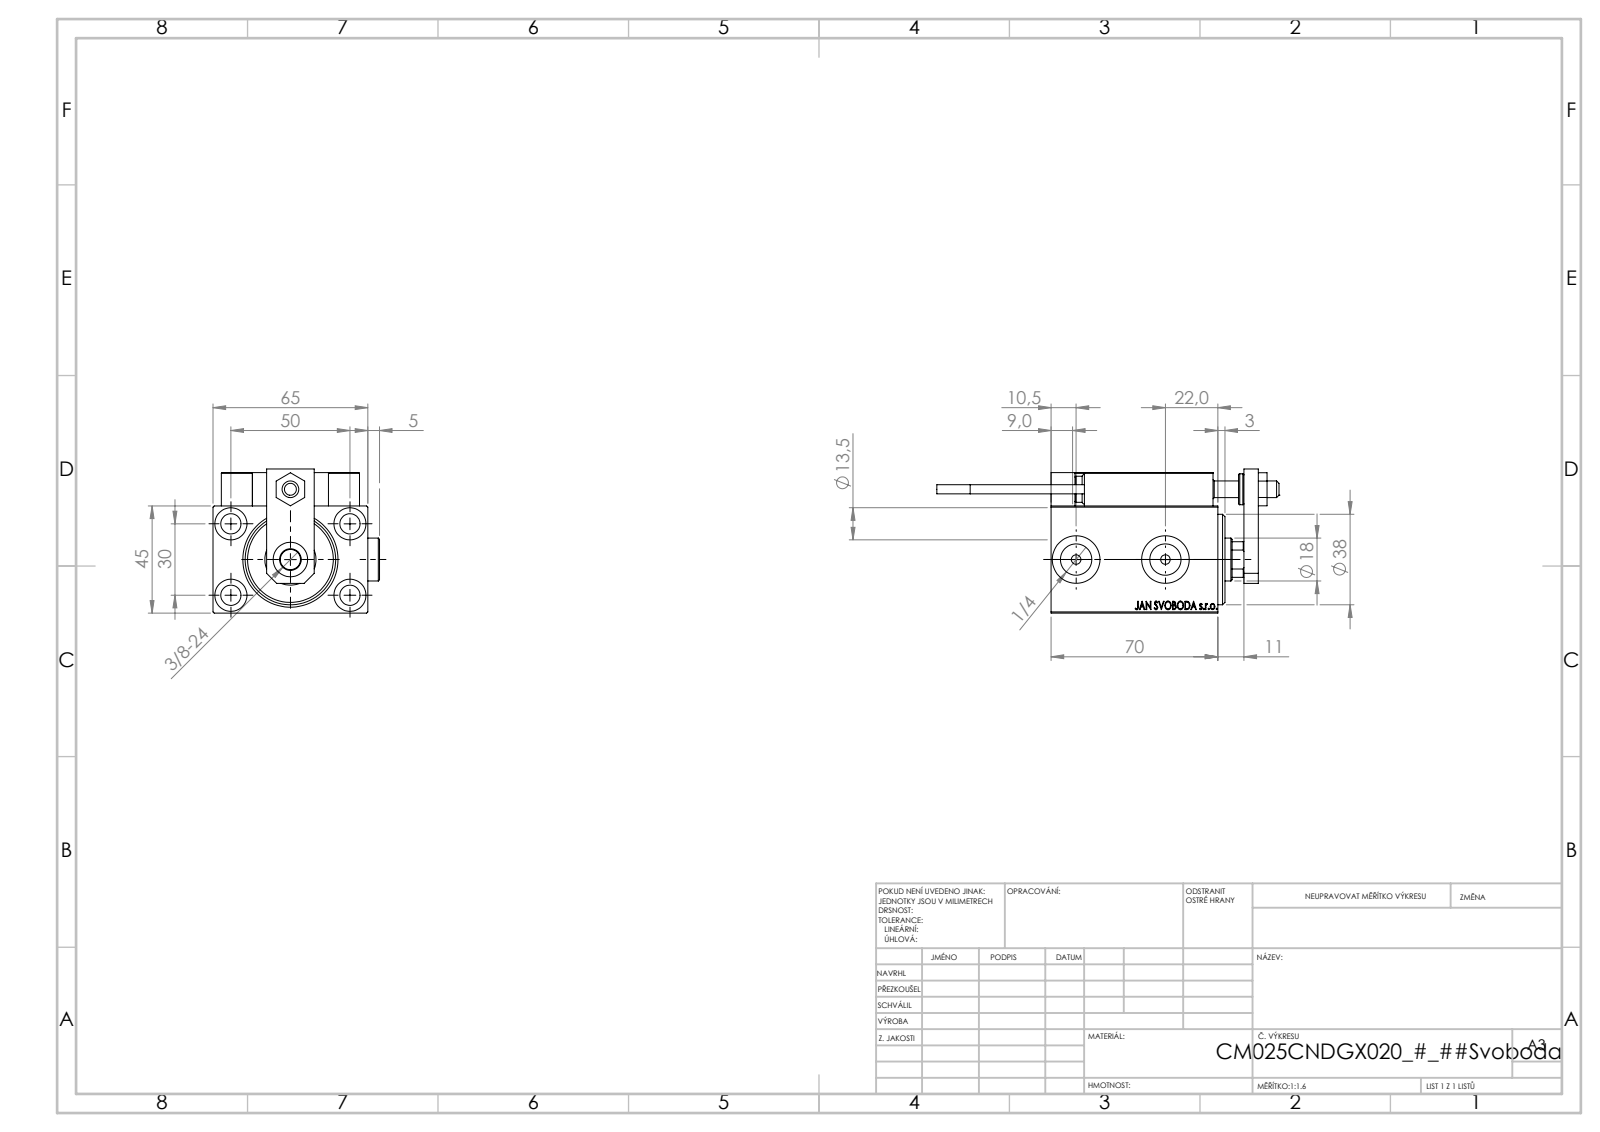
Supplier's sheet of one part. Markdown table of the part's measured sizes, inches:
| quantity | value |
| --- | --- |
| part name | ALLEN BOLT D8; V450CM_C_VCP; V450CM_C_Body; SWITCH_X_FRONT_BACK (+7 more) |
| STEP written by | SolidWorks 2019 (CONFIG_CONTROL_DESIGN) |
| units | inches |
| bodies | 25 solids, 1336 faces (594 planar, 204 cylindrical, 538 other) |
| overall size | 5.657 × 2.752 × 2.382 |
| volume | 13.52 in³ |
| surface area | 111.7 in² |
| round holes (diameter × count) | 0.157 × 6, 0.315 × 5, 0.335 × 5, 0.126 × 4, 0.531 × 4, 0.197 × 2, 0.518 × 2, 0.787 × 2, 0.276 × 1, 0.571 × 1, 0.709 × 1, 0.846 × 1 |
| round bosses / shafts (diameter × count) | 0.709 × 2, 0.197 × 2, 0.15 × 2, 0.512 × 1, 0.433 × 1 |
| partial cylindrical surfaces (radius × count) | 0.012 × 30, 0.118 × 2, 0.335 × 1 |
| main face-to-face distances | 1.772, 2.323, 0.551, 2.559, 0.236, 0.197, 0.118, 0.748, 0.512, 0.276 |
| hole center spacings | 1.148, 0.448, 0.787, 0.87, 1.138, 1.165, 1.169, 1.181 |
